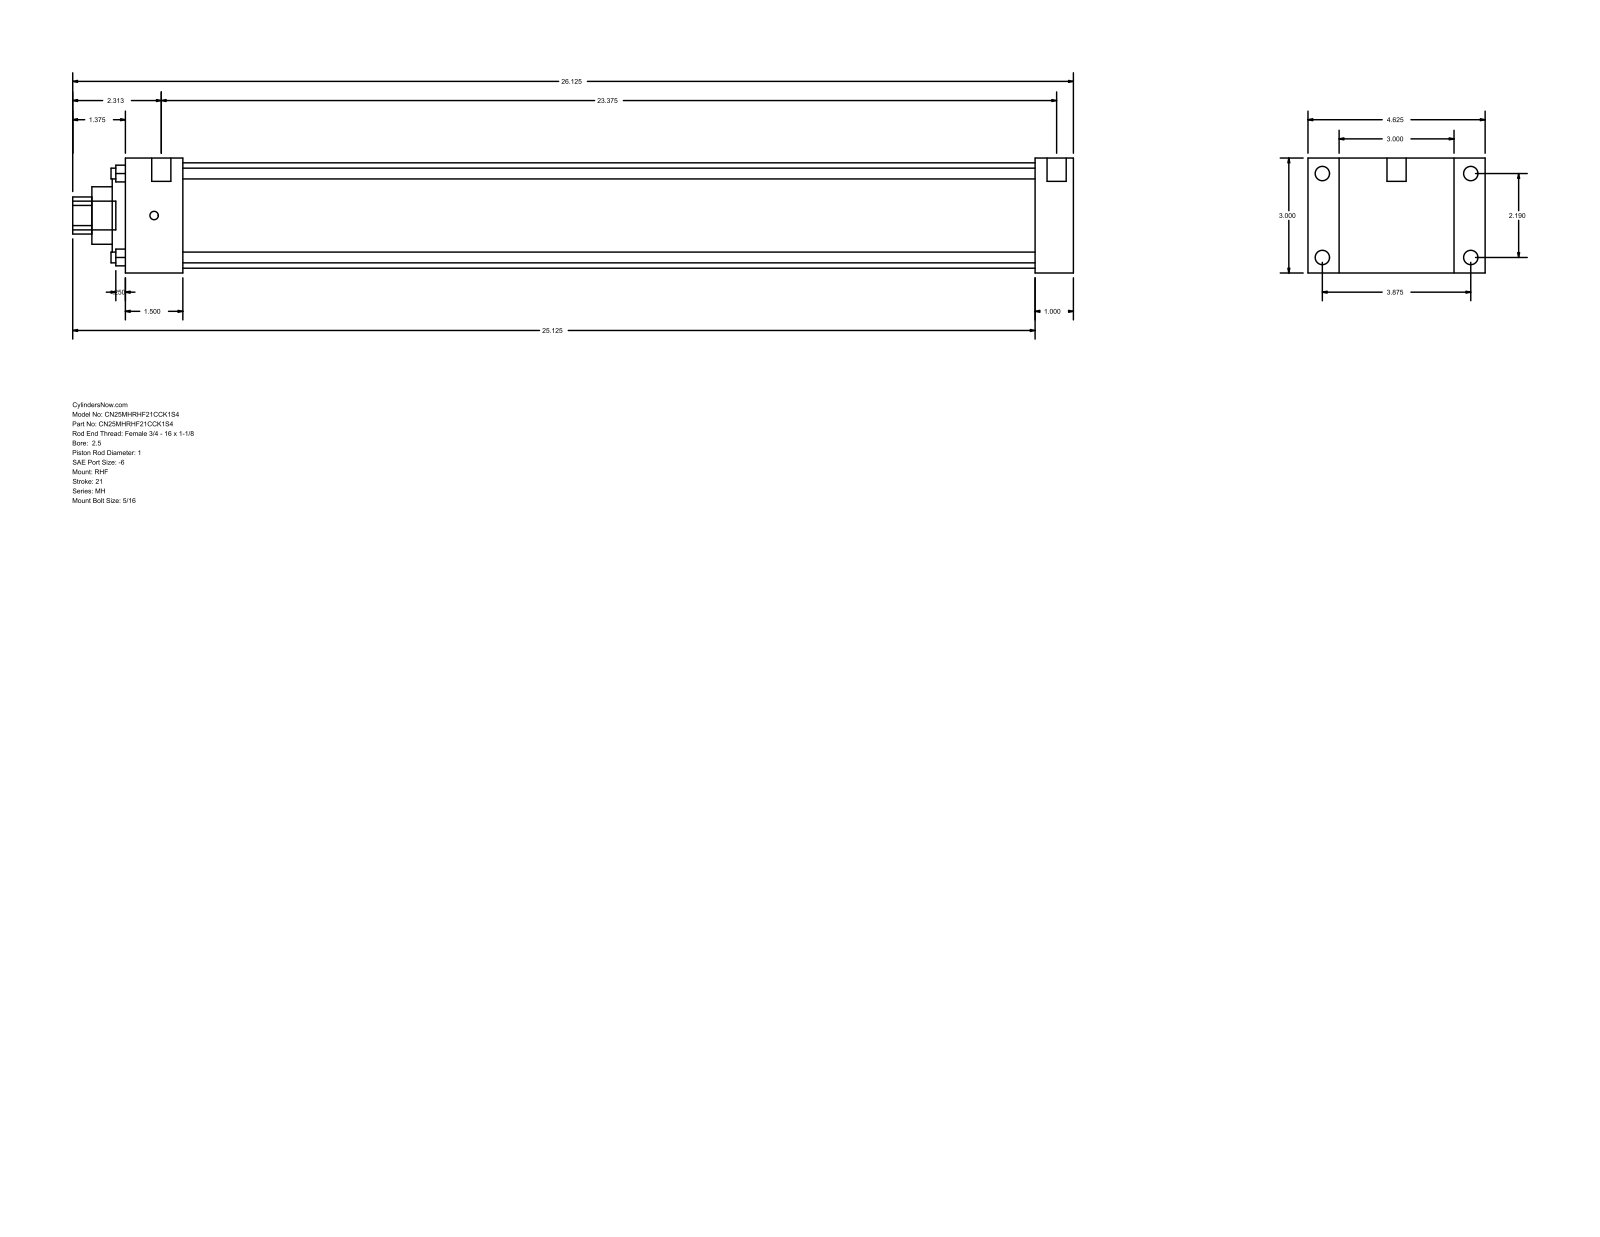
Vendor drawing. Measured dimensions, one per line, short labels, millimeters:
name: MH_RHF__0250_1
written by: GSSL Pune (CONFIG_CONTROL_DESIGN)
unit: mm
bodies: 0 solids, 90 faces (61 planar, 29 cylindrical, 0 other)
size: 663.58 × 117.47 × 76.2
holes: 4× ⌀7.14, 1× ⌀25.4, 1× ⌀38.1, 1× ⌀60.33, 1× ⌀69.85
bosses: 4× ⌀9.53, 4× ⌀5.56, 2× ⌀12.7, 1× ⌀19.05
rounds: 1× R12.29
face distances: 76.2, 25.41, 20.64, 96.84, 603.25, 628.66, 117.48, 38.11, 565.14, 590.55
hole spacings: 39.33, 55.62, 78.66
